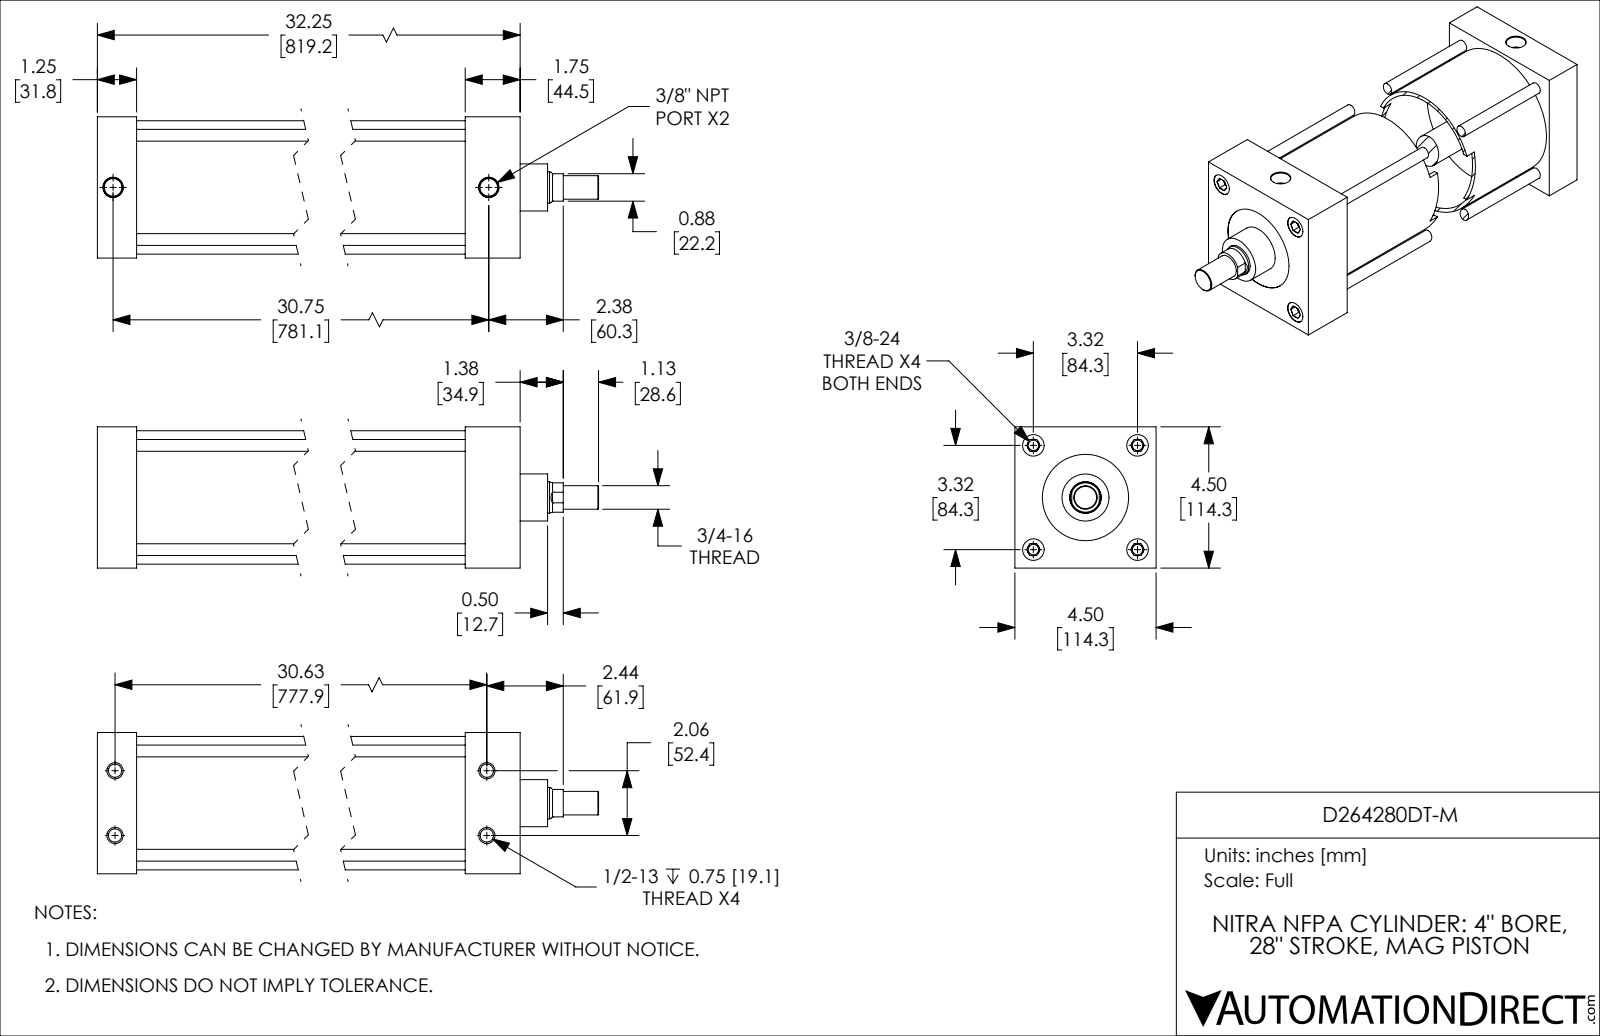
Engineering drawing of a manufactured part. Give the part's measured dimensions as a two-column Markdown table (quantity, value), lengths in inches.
| quantity | value |
| --- | --- |
| part name | D264280DT-M_PISTON_KK1; D264280DT-M_BODY; D264280DT-M |
| STEP written by | SolidWorks 2019 (CONFIG_CONTROL_DESIGN) |
| units | inches |
| bodies | 2 solids, 198 faces (58 planar, 62 cylindrical, 78 other) |
| overall size | 34.75 × 4.5 × 4.5 |
| volume | 158.7 in³ |
| surface area | 1 199 in² |
| round holes (diameter × count) | 0.332 × 4, 0.422 × 4, 0.687 × 4, 0.562 × 2, 1.001 × 1, 2.75 × 1, 4.001 × 1 |
| round bosses / shafts (diameter × count) | 0.375 × 4, 4.251 × 1, 3.999 × 1, 1.5 × 1, 0.999 × 1, 0.75 × 1 |
| partial cylindrical surfaces (radius × count) | 0.469 × 1 |
| main face-to-face distances | 1.25, 4.5, 30.5, 29.25, 32.25, 31, 1.75, 2.5, 28, 29.75 |
| hole center spacings | 2.347, 3.32, 30.705, 1.033, 4.695, 30.625, 30.694, 1.034 |
